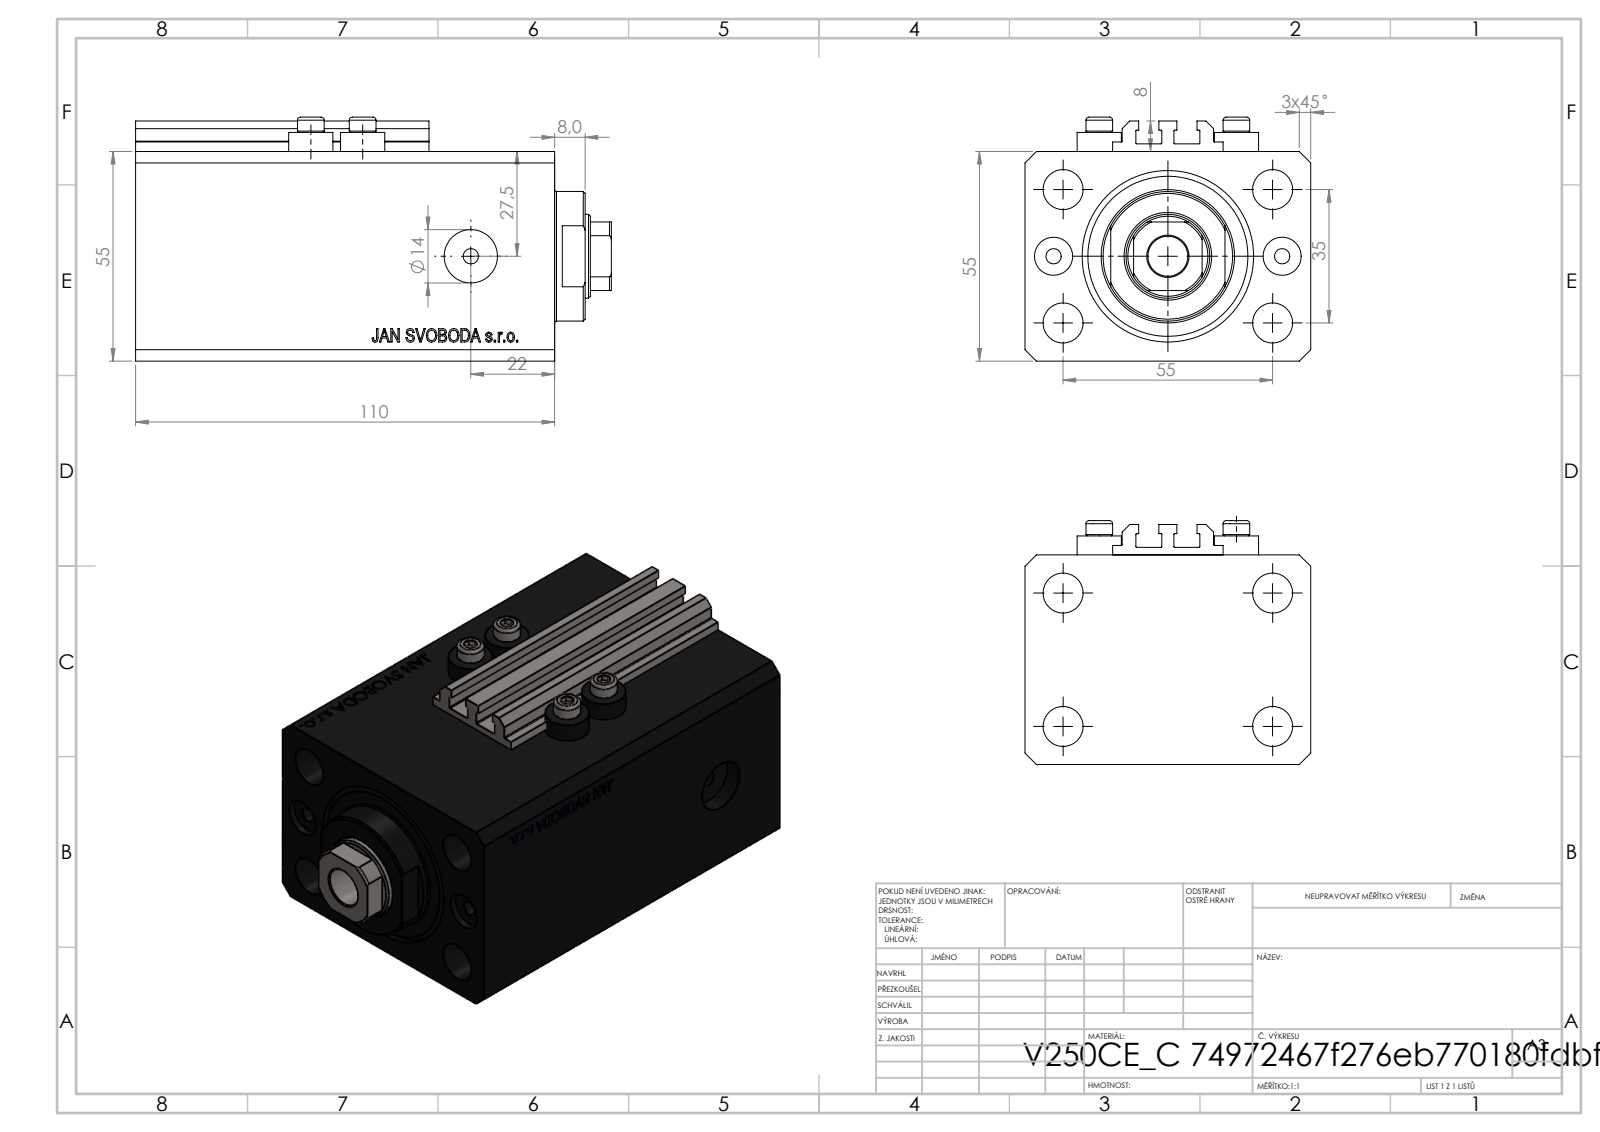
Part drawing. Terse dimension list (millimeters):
name: V250CE_C_VCP; ALLEN BOLT V250CE; V250CE_VC_C; V250CE_C_Body
written by: SolidWorks 2019 (CONFIG_CONTROL_DESIGN)
unit: mm
bodies: 8 solids, 1033 faces (503 planar, 86 cylindrical, 444 other)
size: 124.9 × 75 × 64
volume: 408 868 mm³; area: 93 773 mm²
holes: 8× ⌀4, 5× ⌀10.5, 2× ⌀10, 2× ⌀14, 1× ⌀22, 1× ⌀32, 1× ⌀45
bosses: 4× ⌀11.6, 4× ⌀7, 1× ⌀34
rounds: 10× R0.2, 1× R10.5
face distances: 55, 75, 110, 82.9, 27.1, 9.9, 73, 100.1, 3, 8
hole spacings: 17.68, 32.6, 60.1, 13.6, 30, 35, 36, 38.48
